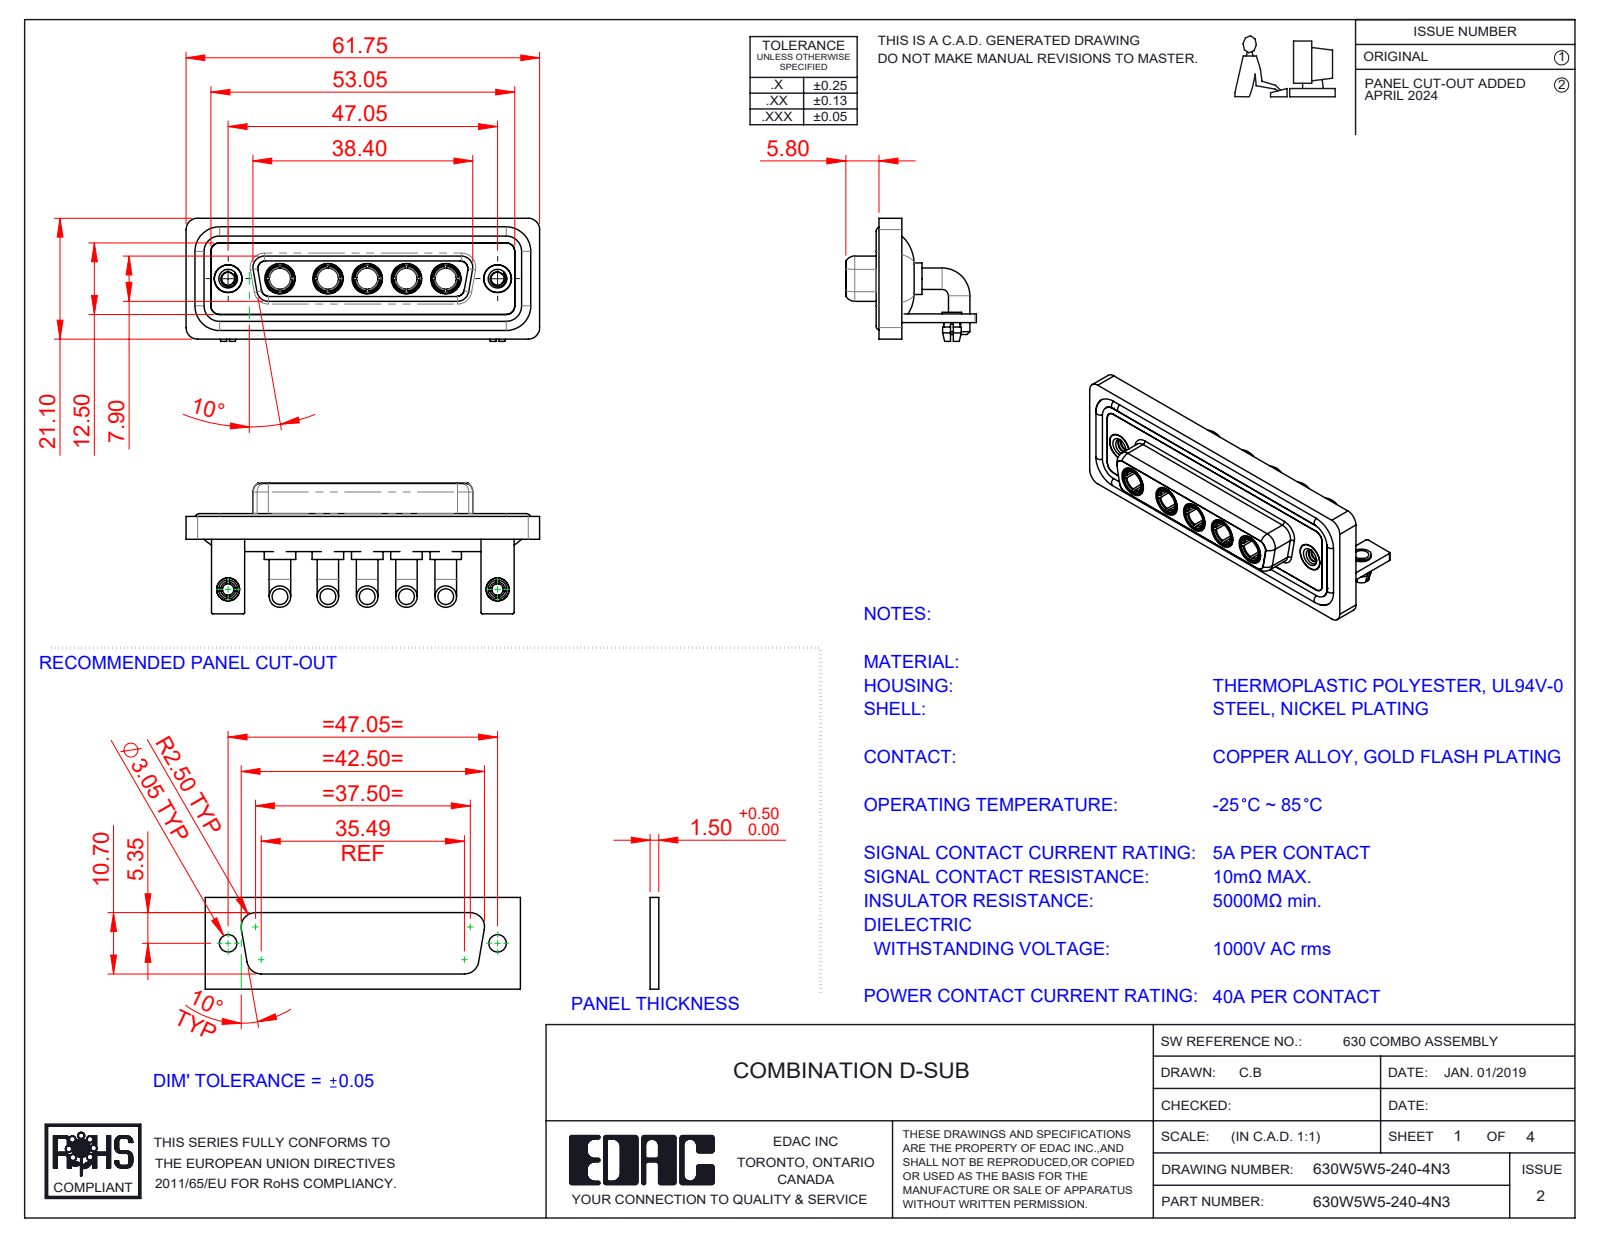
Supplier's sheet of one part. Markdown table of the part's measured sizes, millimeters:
| quantity | value |
| --- | --- |
| part name | 630Combo Housing_5W5; 630Combo Threaded Rivet_2; 630Combo Stabilizer Bracket_50 Contacts; 630Combo Board Lock_50 Contacts (+5 more) |
| STEP written by | SolidWorks 2023 (CONFIG_CONTROL_DESIGN) |
| units | millimeters |
| bodies | 21 solids, 916 faces (318 planar, 369 cylindrical, 229 other) |
| overall size | 61.75 × 22.8 × 21.5 |
| volume | 9 201 mm³ |
| surface area | 14 978 mm² |
| round holes (diameter × count) | 4.85 × 7, 3.7 × 5, 5.3 × 5, 2 × 2, 2.26 × 2, 2.5 × 2, 3.2 × 2, 4 × 2, 4.05 × 2, 5 × 2 |
| round bosses / shafts (diameter × count) | 3.75 × 10, 5.5 × 5, 5.2 × 5, 4.96 × 5, 4.75 × 5, 1.6 × 4, 4.95 × 2, 4.8 × 2 |
| partial cylindrical surfaces (radius × count) | 2 × 19, 1.5 × 18, 0.25 × 16, 1.35 × 8, 1.6 × 8, 0.5 × 5, 2.1 × 5, 0.6 × 4 |
| main face-to-face distances | 0.4, 1.8, 2.9, 3.7, 1.5, 4.1, 1.1, 1.4, 1.6, 2.5 |
| hole center spacings | 6.86, 9.04, 38.01, 47.05, 6.87, 8.38, 13.72, 13.73 |
